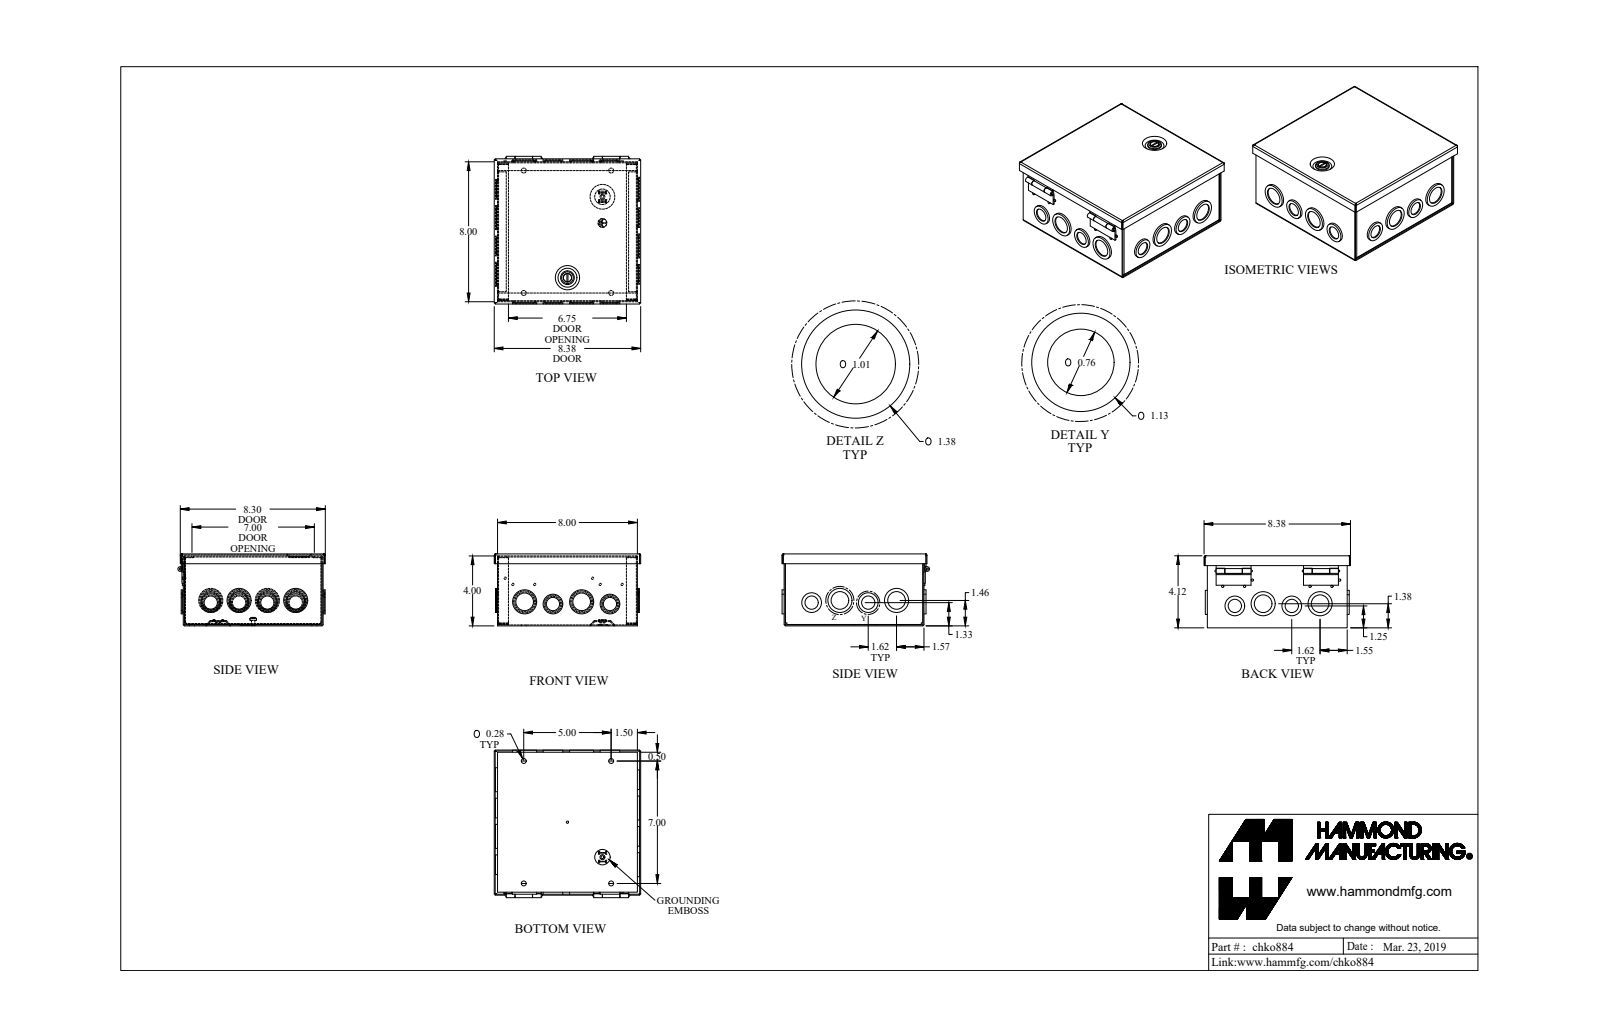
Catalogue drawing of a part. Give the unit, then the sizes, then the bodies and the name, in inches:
Units: inches
Overall size (bounding box): 8.443 × 8.38 × 4.118
Round holes (diameter × count): ⌀1.011 ×12, ⌀0.761 ×6, ⌀1.261 ×6, ⌀0.281 ×4, ⌀0.125 ×1, ⌀0.17 ×1, ⌀0.319 ×1, ⌀0.476 ×1, ⌀0.5 ×1
Round bosses / shafts (diameter × count): ⌀0.131 ×8, ⌀1.125 ×6, ⌀1.125 ×6, ⌀1.375 ×4, ⌀0.875 ×4, ⌀0.875 ×4, ⌀1.375 ×2, ⌀0.787 ×1
Partial cylindrical surfaces — rounded edges, fillets, slot ends (radius × count): R0.029 ×16, R0.086 ×16, R0.057 ×8, R0.012 ×4, R0.1 ×4, R0.036 ×2, R0.079 ×2, R0.25 ×2
Main face-to-face distances: 0.057, 4.061, 7.943, 8, 4.118, 4.004, 7.886, 3.943, 0.118, 0.08
Hole centre spacings: 1.625, 0.125, 1.62, 3.24, 3.242, 1.62, 1.624, 3.26
Volume: 18.78 in³ · Surface area: 661.1 in²
Bodies: 12 solids, 679 faces (336 planar, 300 cylindrical, 43 other)
Part name (STEP PRODUCT): CHKO884_Default
STEP written by: SolidWorks 2019 (CONFIG_CONTROL_DESIGN)
